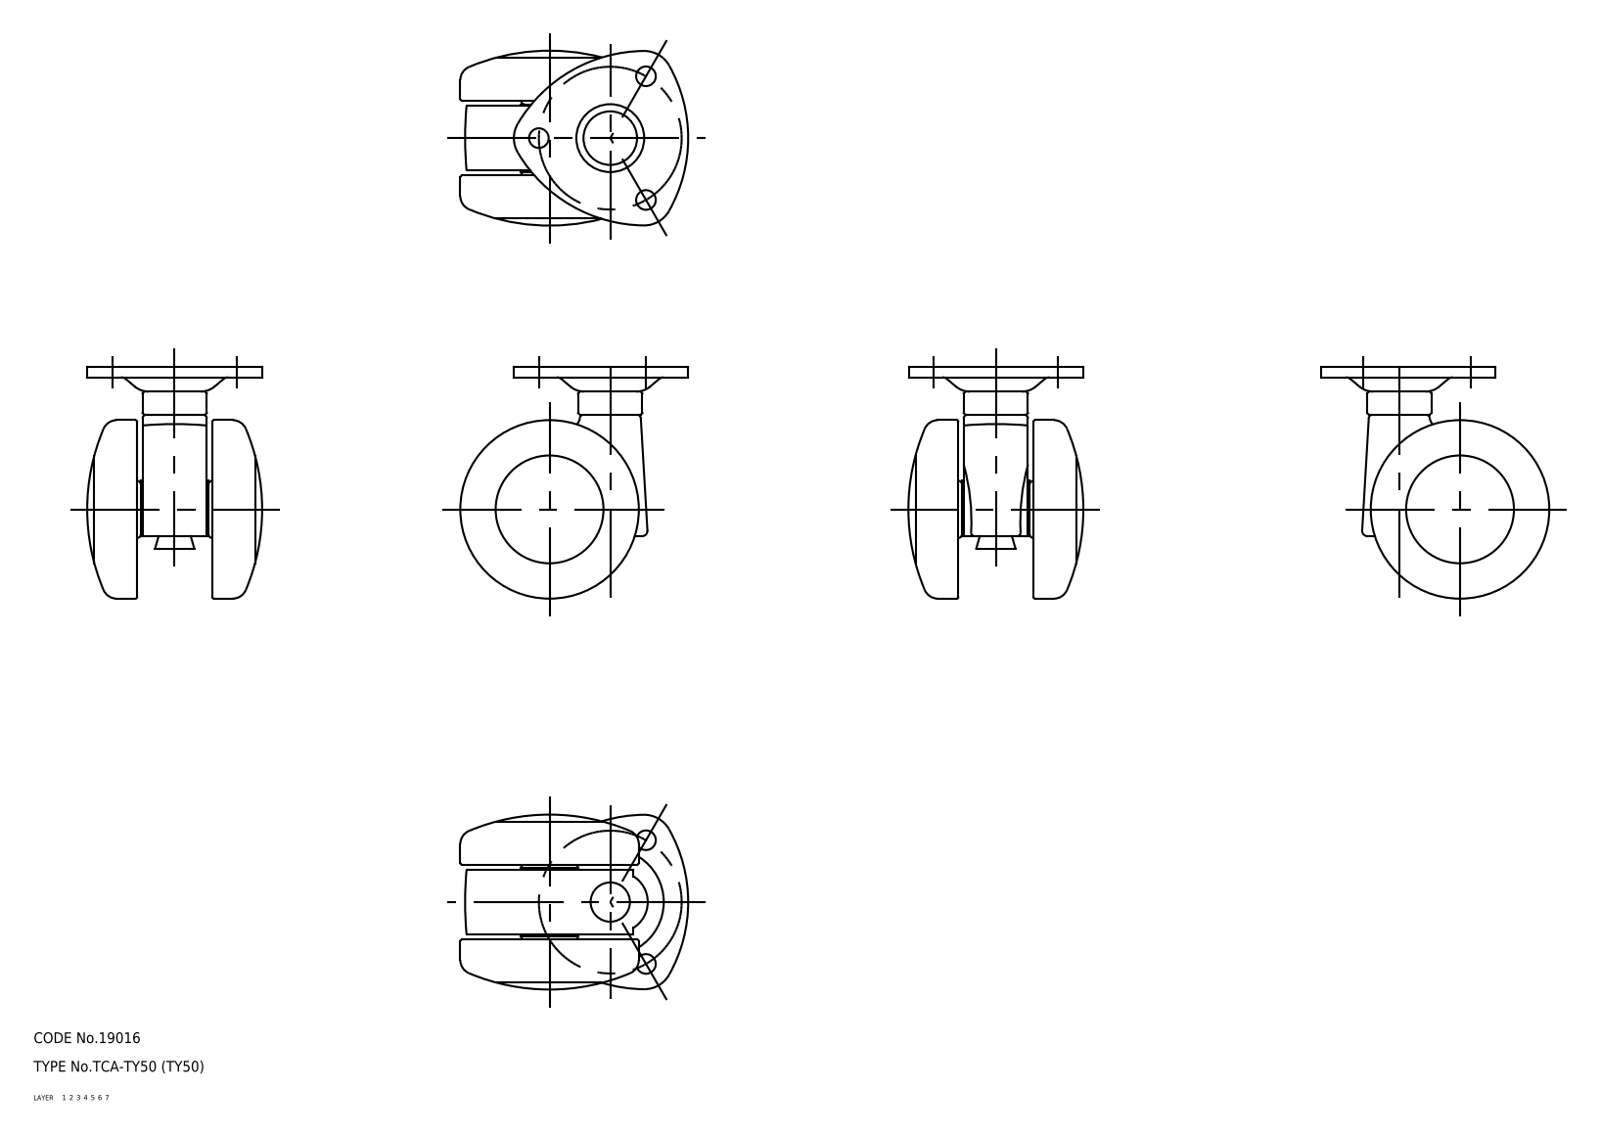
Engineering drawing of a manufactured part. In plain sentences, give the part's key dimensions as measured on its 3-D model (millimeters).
The part is named "wheel; mounting plate; main shaft; TY50_10766_36". Its 3-D file was written by "CADfix (AUTOMOTIVE_DESIGN)". It is 5 solids with 134 faces: 0 planar, 0 cylindrical and 134 other. Overall it measures 65 by 63.82 by 49 millimeters. Its volume is 68 019 cubic millimeters and its surface area 30 023 square millimeters.
